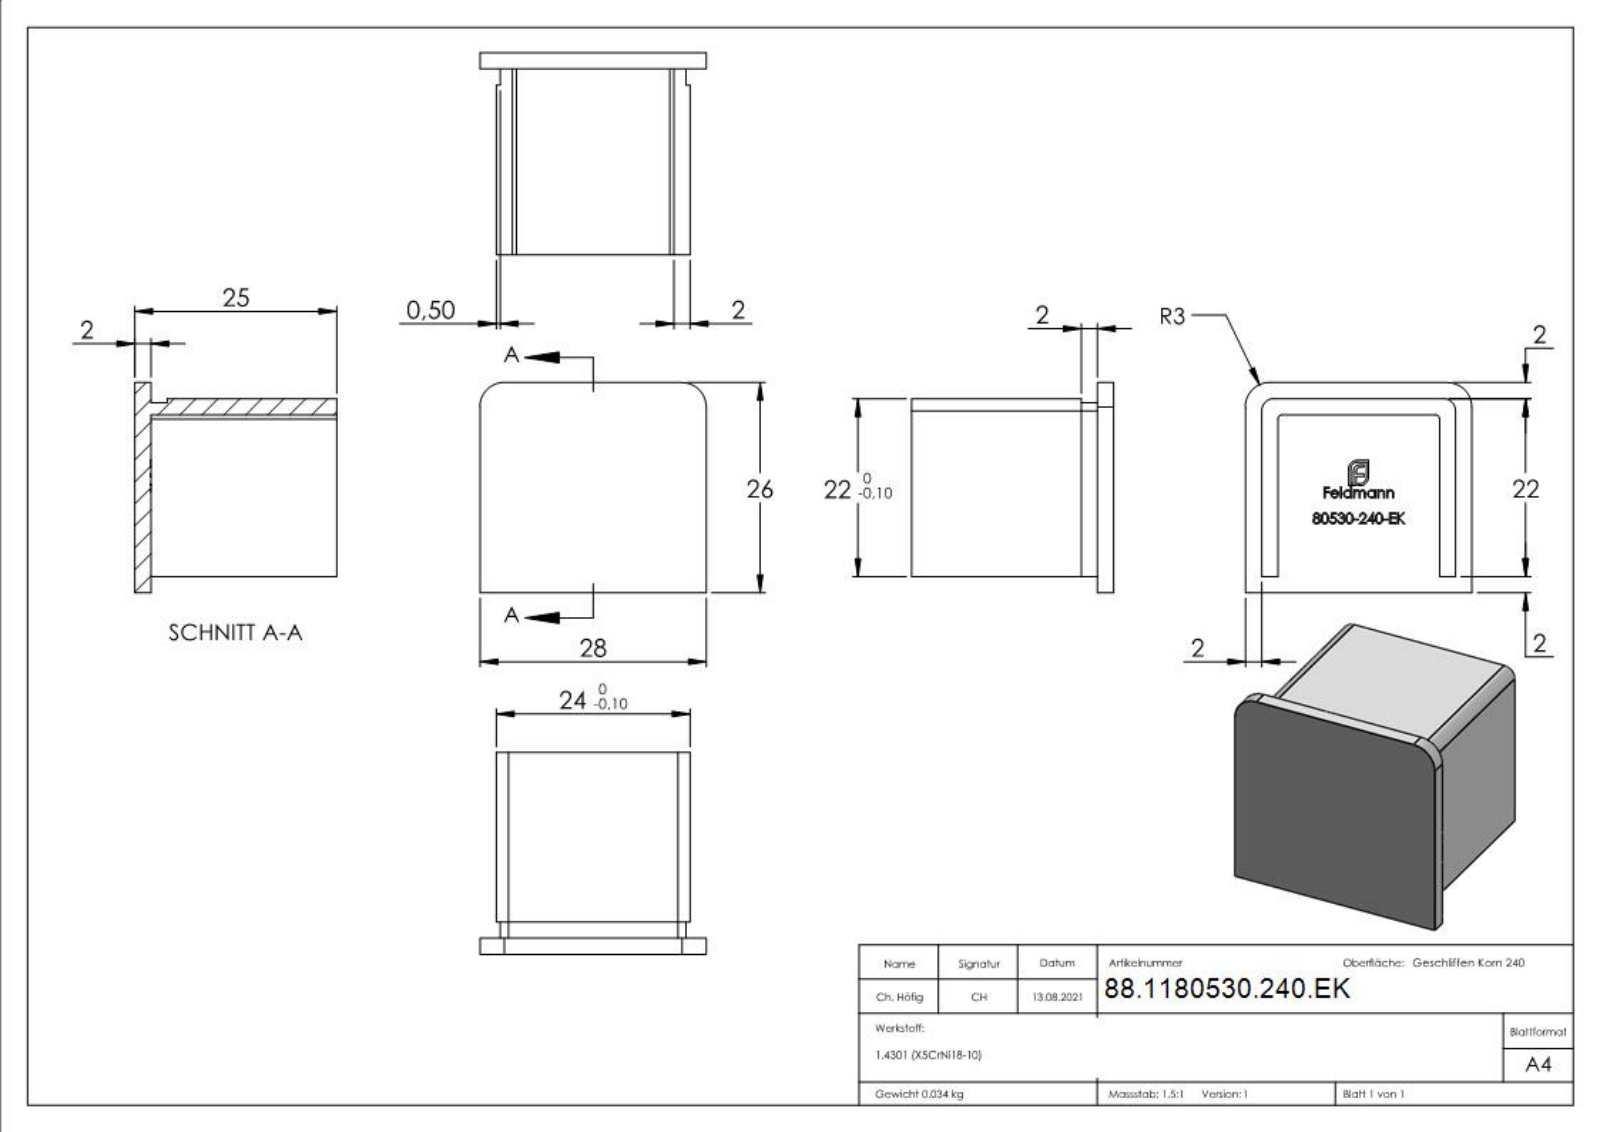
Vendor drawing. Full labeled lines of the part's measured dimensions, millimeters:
Part name (STEP PRODUCT): 80530-240-EK
STEP written by: SolidWorks 2018 (CONFIG_CONTROL_DESIGN)
Units: millimetres
Bodies: 1 solid, 336 faces (188 planar, 8 cylindrical, 140 other)
Overall size (bounding box): 28 × 26 × 25
Volume: 4 306 mm³ · Surface area: 4 731 mm²
Partial cylindrical surfaces — rounded edges, fillets, slot ends (radius × count): R0.5 ×2, R1 ×2, R1.5 ×2, R3 ×2
Main face-to-face distances: 2, 22, 24, 20, 4, 23, 26, 25, 1.5, 2.5
